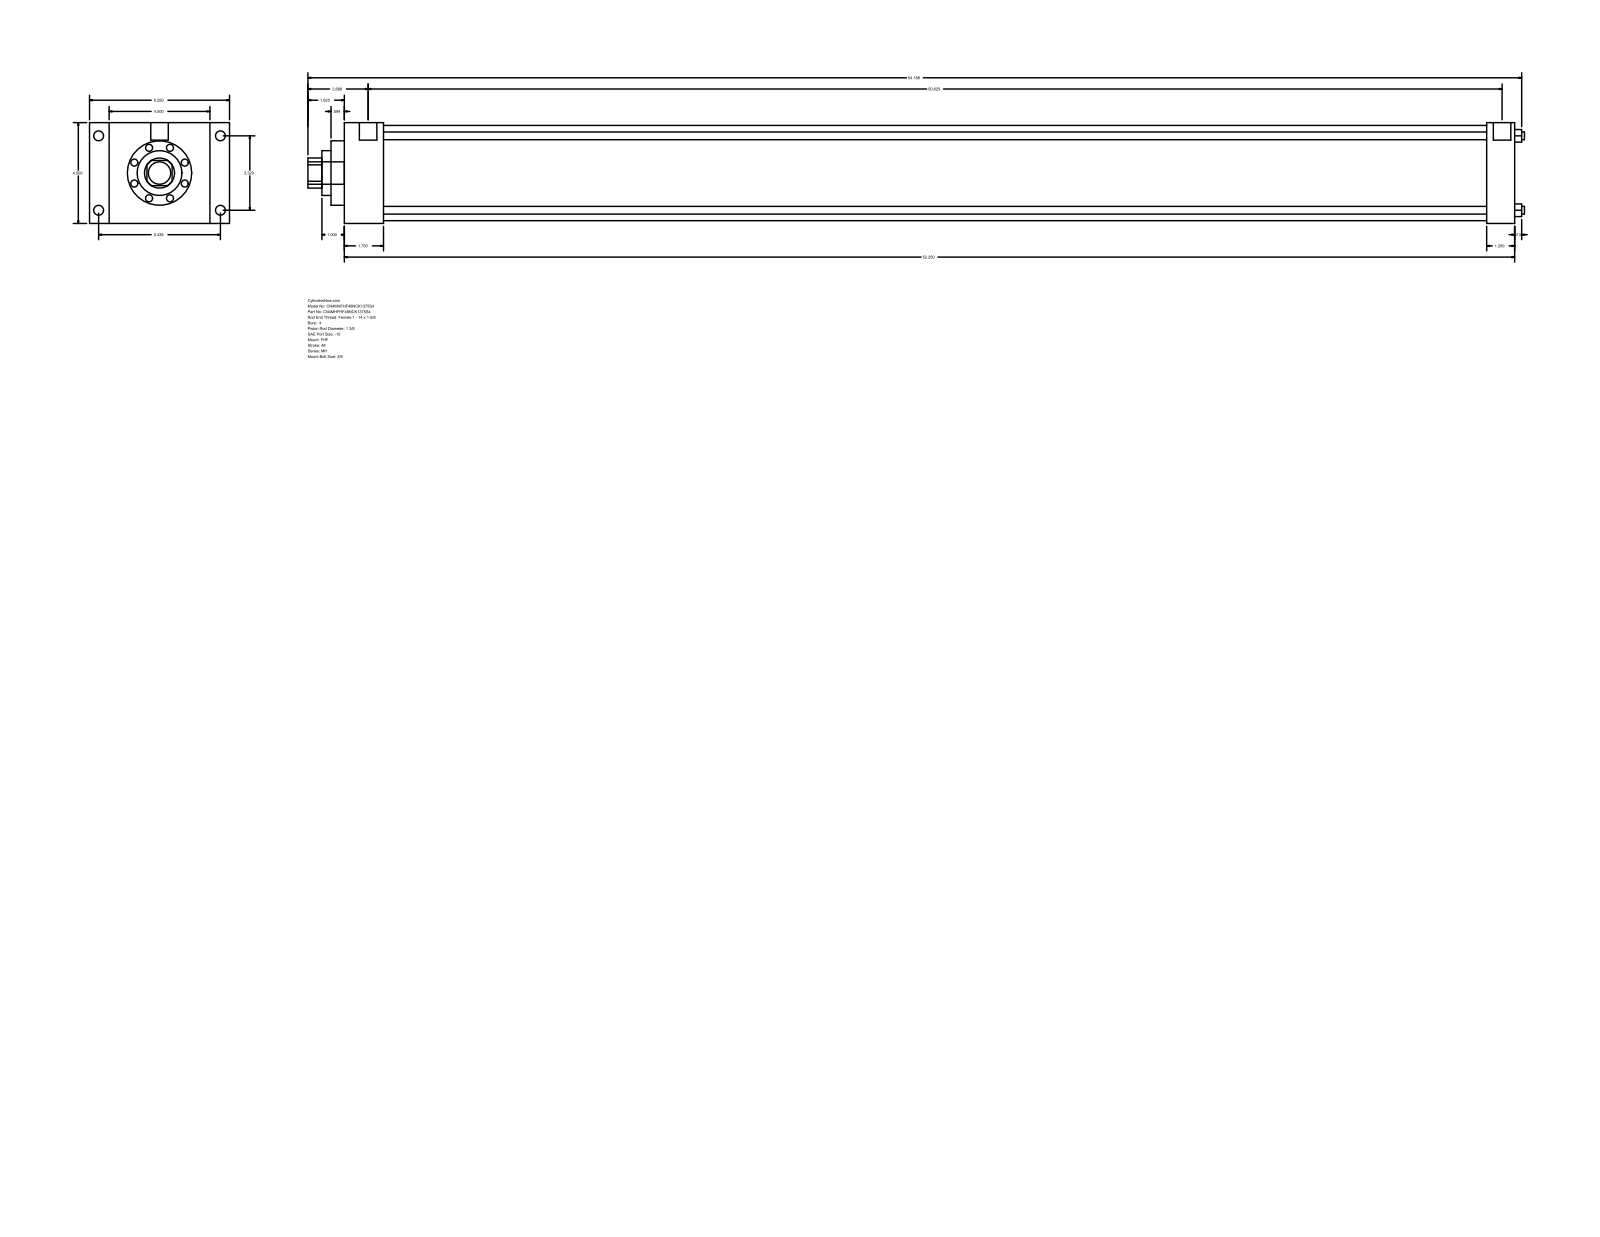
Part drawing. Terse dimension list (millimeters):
name: MH_FHF__0400_1.375
written by: GSSL Pune (CONFIG_CONTROL_DESIGN)
unit: mm
bodies: 0 solids, 90 faces (61 planar, 29 cylindrical, 0 other)
size: 1379.54 × 158.75 × 114.3
holes: 4× ⌀8.76, 1× ⌀34.92, 1× ⌀50.8, 1× ⌀73.03, 1× ⌀107.95
bosses: 4× ⌀11.13, 4× ⌀8.73, 2× ⌀19.84, 1× ⌀25.4
rounds: 1× R17.06
face distances: 114.3, 1327.15, 44.45, 1282.7, 22.23, 136.53, 158.76, 1295.4, 1250.95, 31.75
hole spacings: 59.62, 84.32, 119.25
